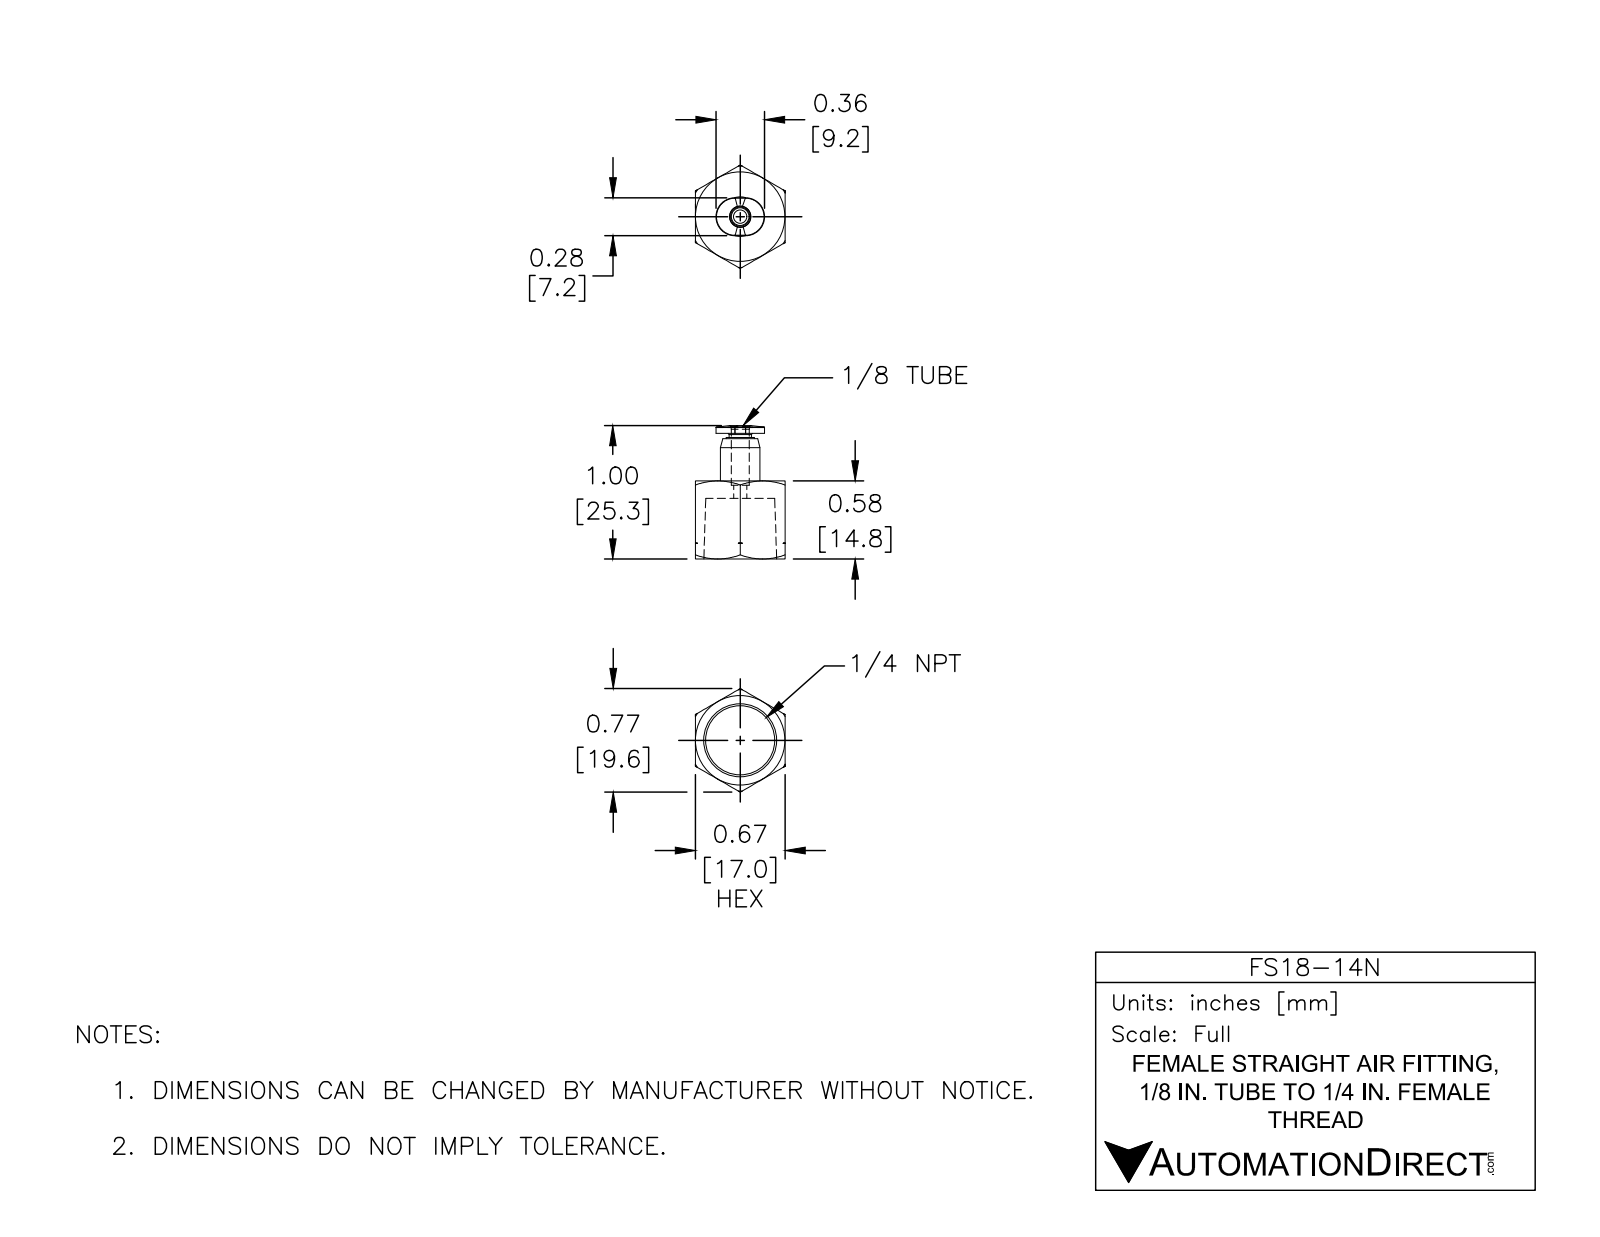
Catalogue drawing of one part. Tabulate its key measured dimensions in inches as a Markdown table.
| quantity | value |
| --- | --- |
| part name | FS18-14N |
| STEP written by | SolidWorks 2015 (CONFIG_CONTROL_DESIGN) |
| units | inches |
| bodies | 1 solid, 78 faces (16 planar, 12 cylindrical, 50 other) |
| overall size | 0.996 × 0.773 × 0.669 |
| volume | 0.145 in³ |
| surface area | 3.493 in² |
| round holes (diameter × count) | 0.098 × 1, 0.134 × 1 |
| round bosses / shafts (diameter × count) | 0.295 × 1, 0.209 × 1, 0.165 × 1 |
| partial cylindrical surfaces (radius × count) | 0.142 × 2 |
| main face-to-face distances | 0.669, 0.13, 0.453, 0.583, 0.937, 0.484, 0.354, 0.445, 0.898, 0.315 |
